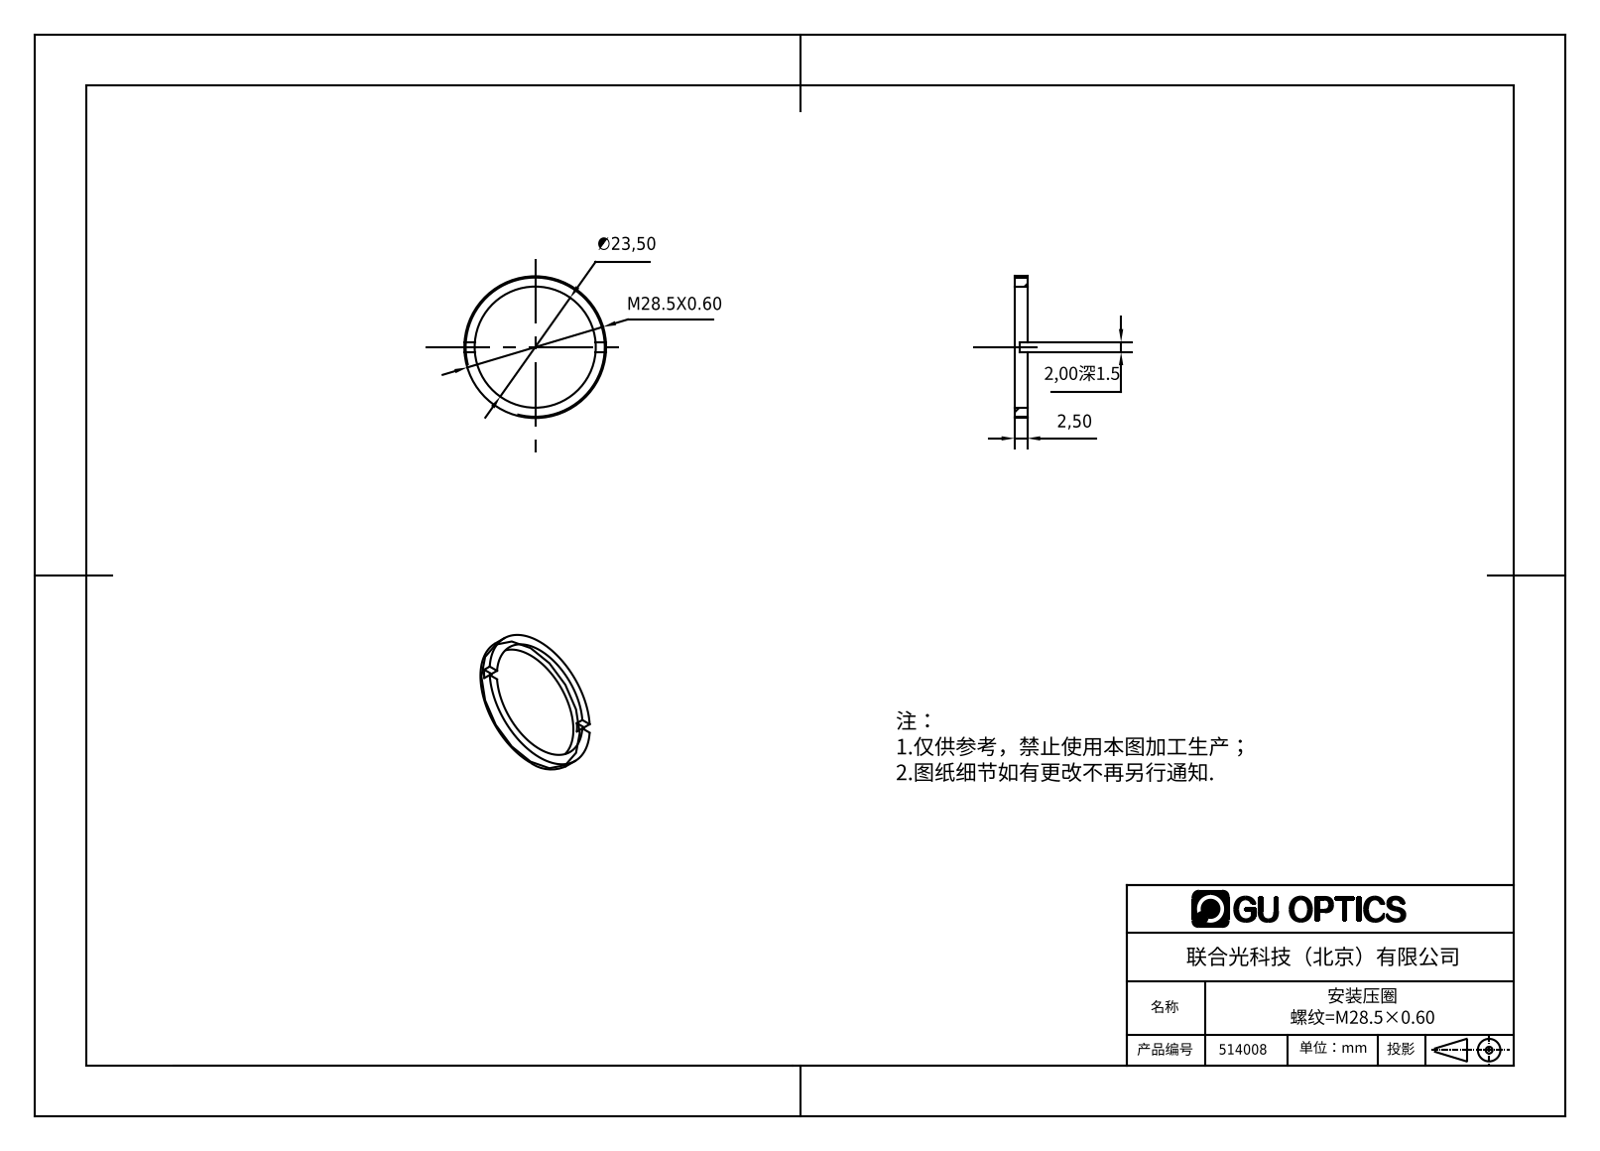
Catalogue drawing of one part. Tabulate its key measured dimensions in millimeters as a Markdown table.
| quantity | value |
| --- | --- |
| part name | 514008 |
| STEP written by | SolidWorks 2016 (AUTOMOTIVE_DESIGN) |
| units | millimeters |
| bodies | 1 solid, 13 faces (9 planar, 4 cylindrical, 0 other) |
| overall size | 27.5 × 27.5 × 2.5 |
| volume | 389 mm³ |
| surface area | 721 mm² |
| round holes (diameter × count) | 23.5 × 1 |
| round bosses / shafts (diameter × count) | 27.5 × 1 |
| main face-to-face distances | 2.5, 1, 1.5, 2 |
